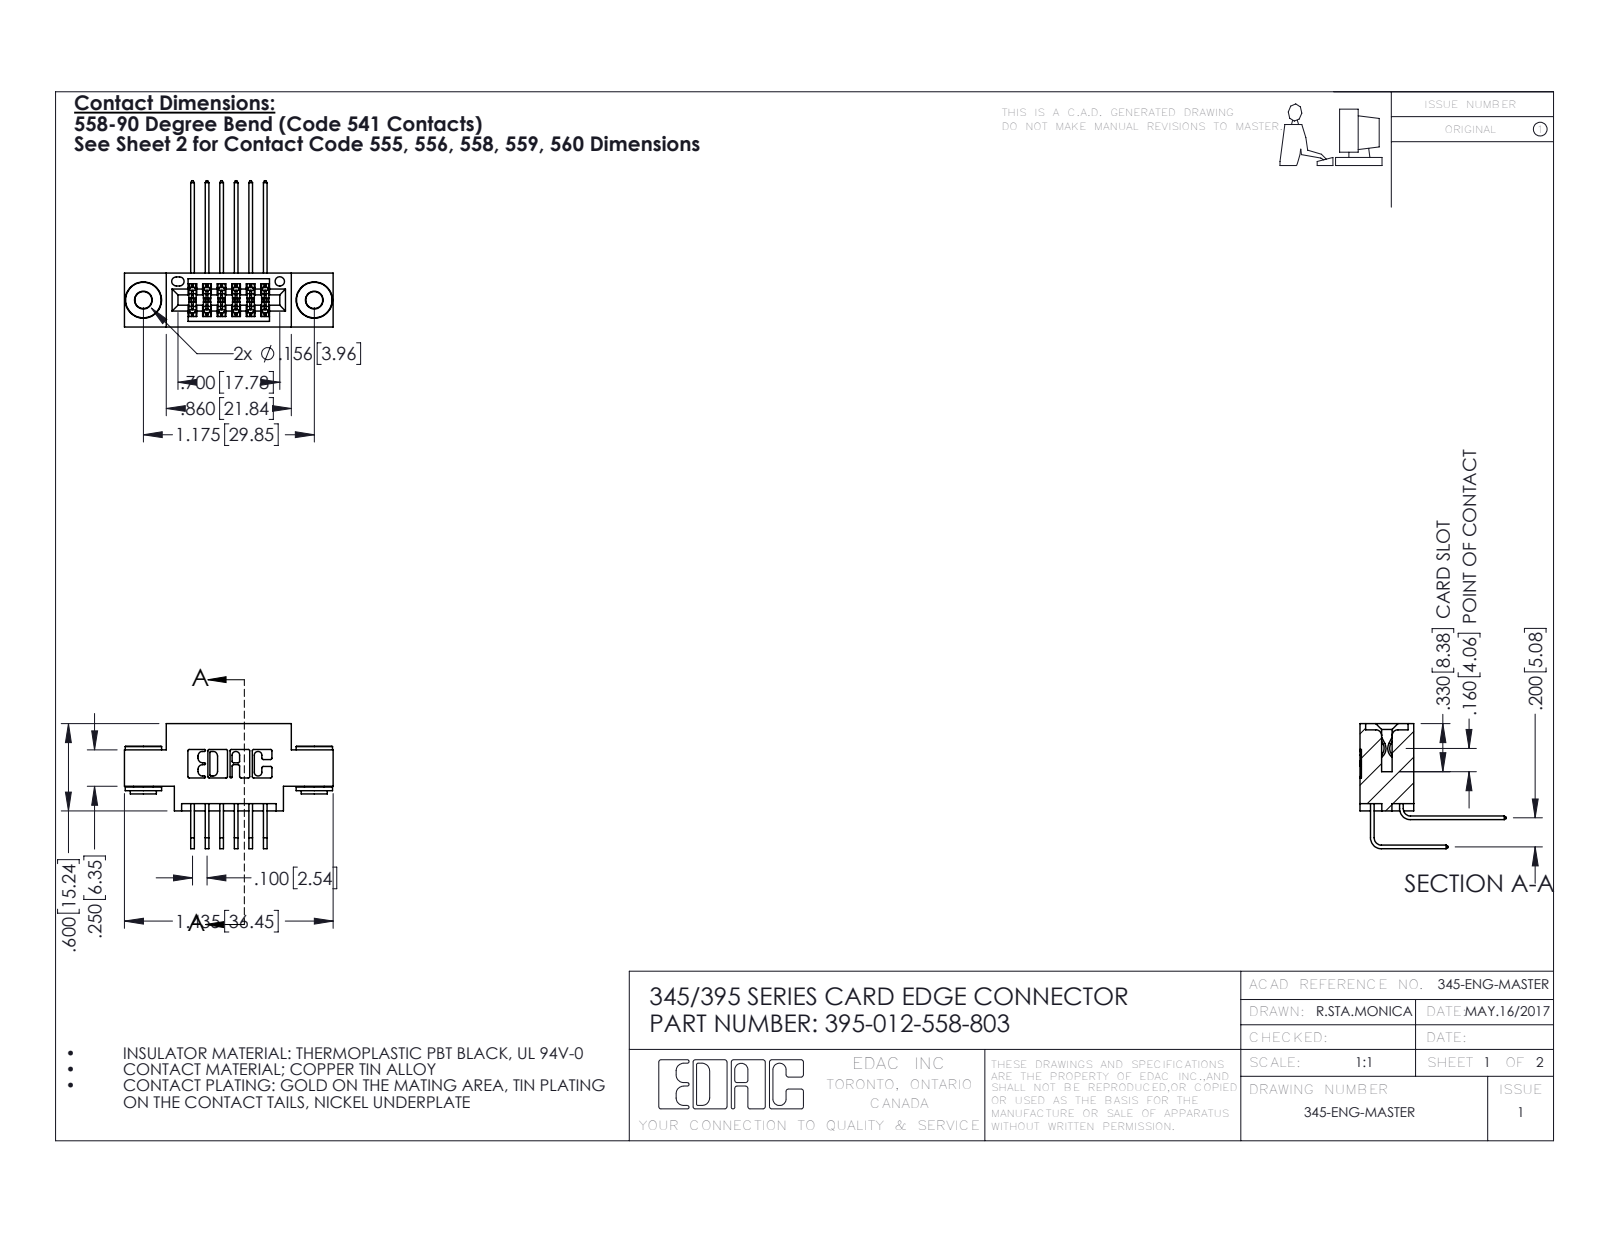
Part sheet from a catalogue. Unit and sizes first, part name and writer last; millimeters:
Units: millimetres
Overall size (bounding box): 36.4 × 25.5 × 21.8
Round holes (diameter × count): ⌀2.9 ×2, ⌀4 ×2, ⌀1.6 ×1
Round bosses / shafts (diameter × count): ⌀6.4 ×2, ⌀4.6 ×2, ⌀3.5 ×2
Partial cylindrical surfaces — rounded edges, fillets, slot ends (radius × count): R0.3 ×22, R0.2 ×19, R0.2 ×6, R0.8 ×6, R0.7 ×3, R0.4 ×2, R0.5 ×2, R0.6 ×2
Main face-to-face distances: 5.1, 9.4, 2.5, 1.8, 7.6, 2.5, 6.9, 0.6, 6.4, 4.4
Hole centre spacings: 6.9, 24, 29.8
Volume: 3 180 mm³ · Surface area: 4 680 mm²
Bodies: 15 solids, 792 faces (514 planar, 270 cylindrical, 8 other)
Part name (STEP PRODUCT): 345-250-002_345-250-002-102; 345-292-001_558 Tail - 2; 345-292-001_558 559 Tail - 1; 395-012-558-803 (+1 more)
STEP written by: SolidWorks 2016 (CONFIG_CONTROL_DESIGN)
